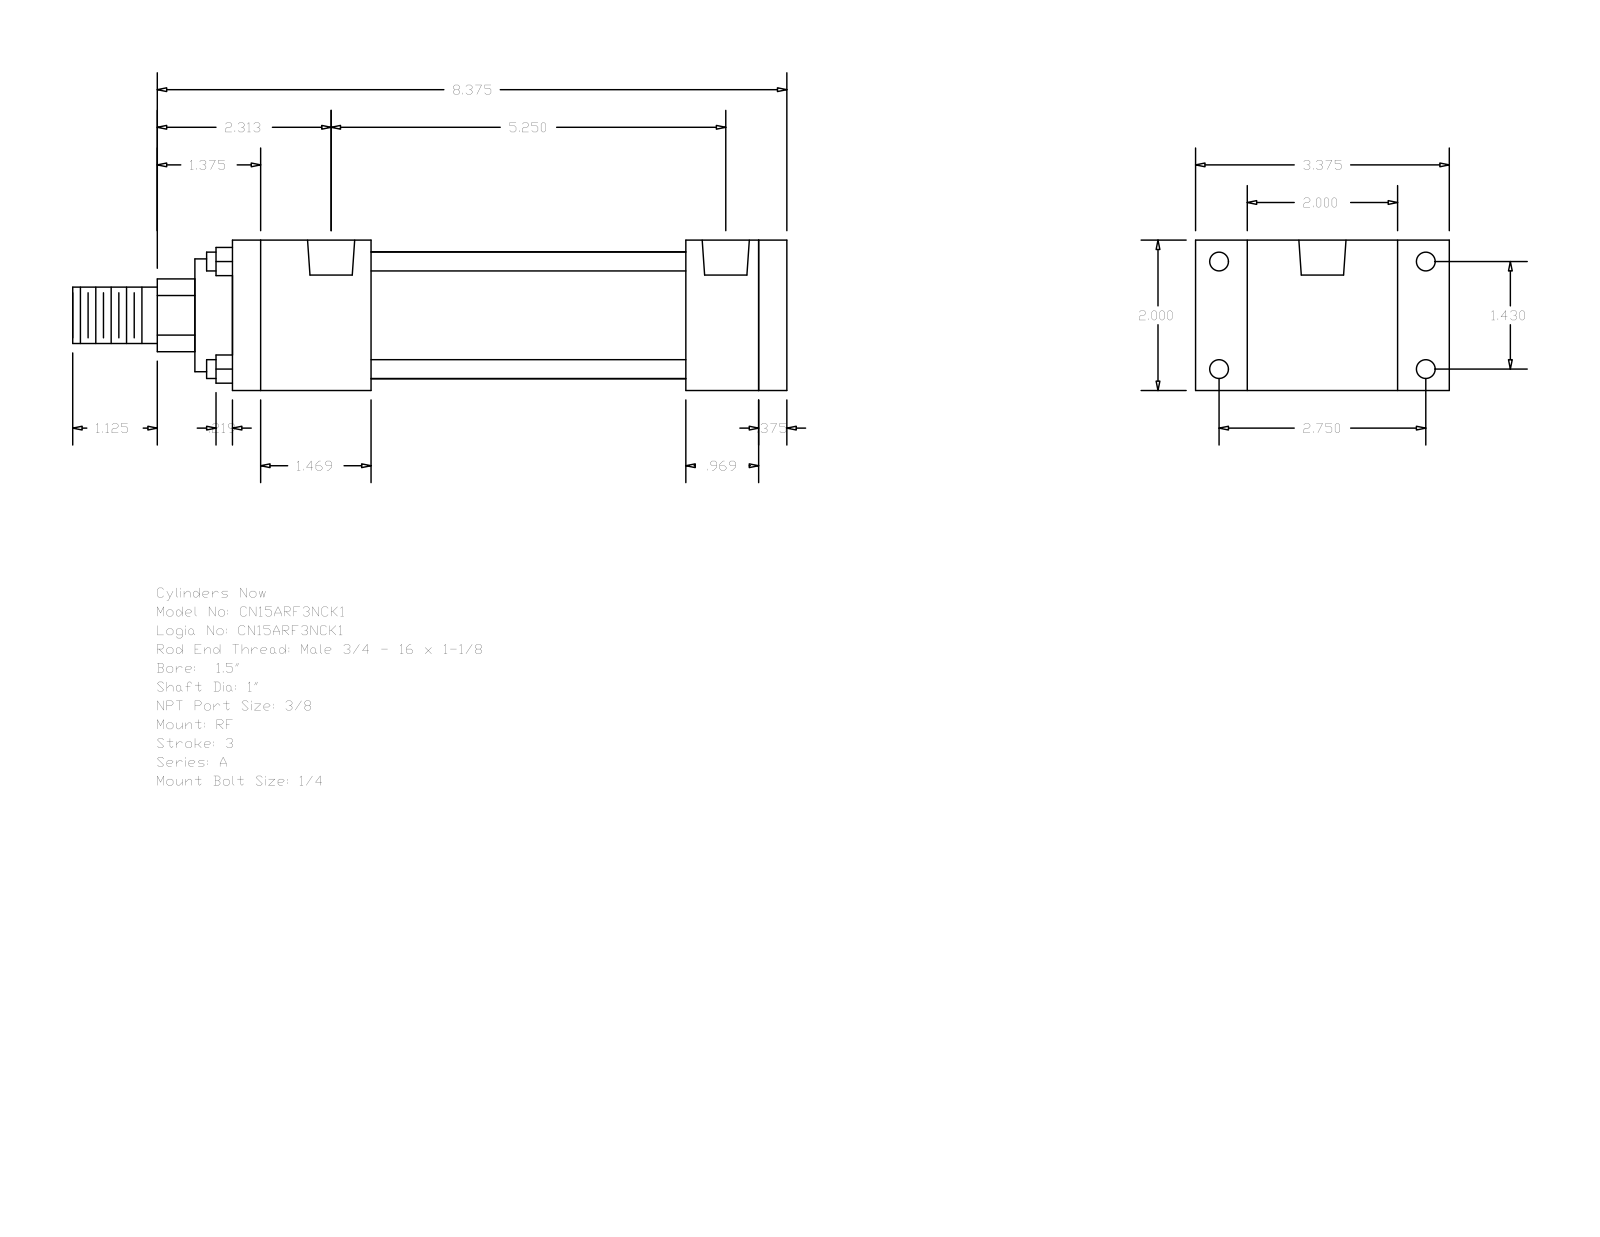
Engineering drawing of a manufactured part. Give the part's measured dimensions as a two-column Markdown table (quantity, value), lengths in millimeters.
| quantity | value |
| --- | --- |
| part name | A_RF__0150_1 |
| STEP written by | GSSL Pune (CONFIG_CONTROL_DESIGN) |
| units | millimeters |
| bodies | 0 solids, 92 faces (64 planar, 28 cylindrical, 0 other) |
| overall size | 241.3 × 85.72 × 50.8 |
| round holes (diameter × count) | 5.56 × 4, 6.35 × 4, 15.93 × 2 |
| round bosses / shafts (diameter × count) | 6.35 × 4, 42.93 × 1, 38.1 × 1, 25.4 × 1, 19.05 × 1 |
| partial cylindrical surfaces (radius × count) | 12.29 × 1 |
| main face-to-face distances | 50.8, 9.52, 177.8, 187.32, 153.19, 24.61, 34.13, 46.83, 106.36, 130.97 |
| hole center spacings | 3.97, 36.32, 69.84, 78.72, 125.41, 129.38, 133.35 |
